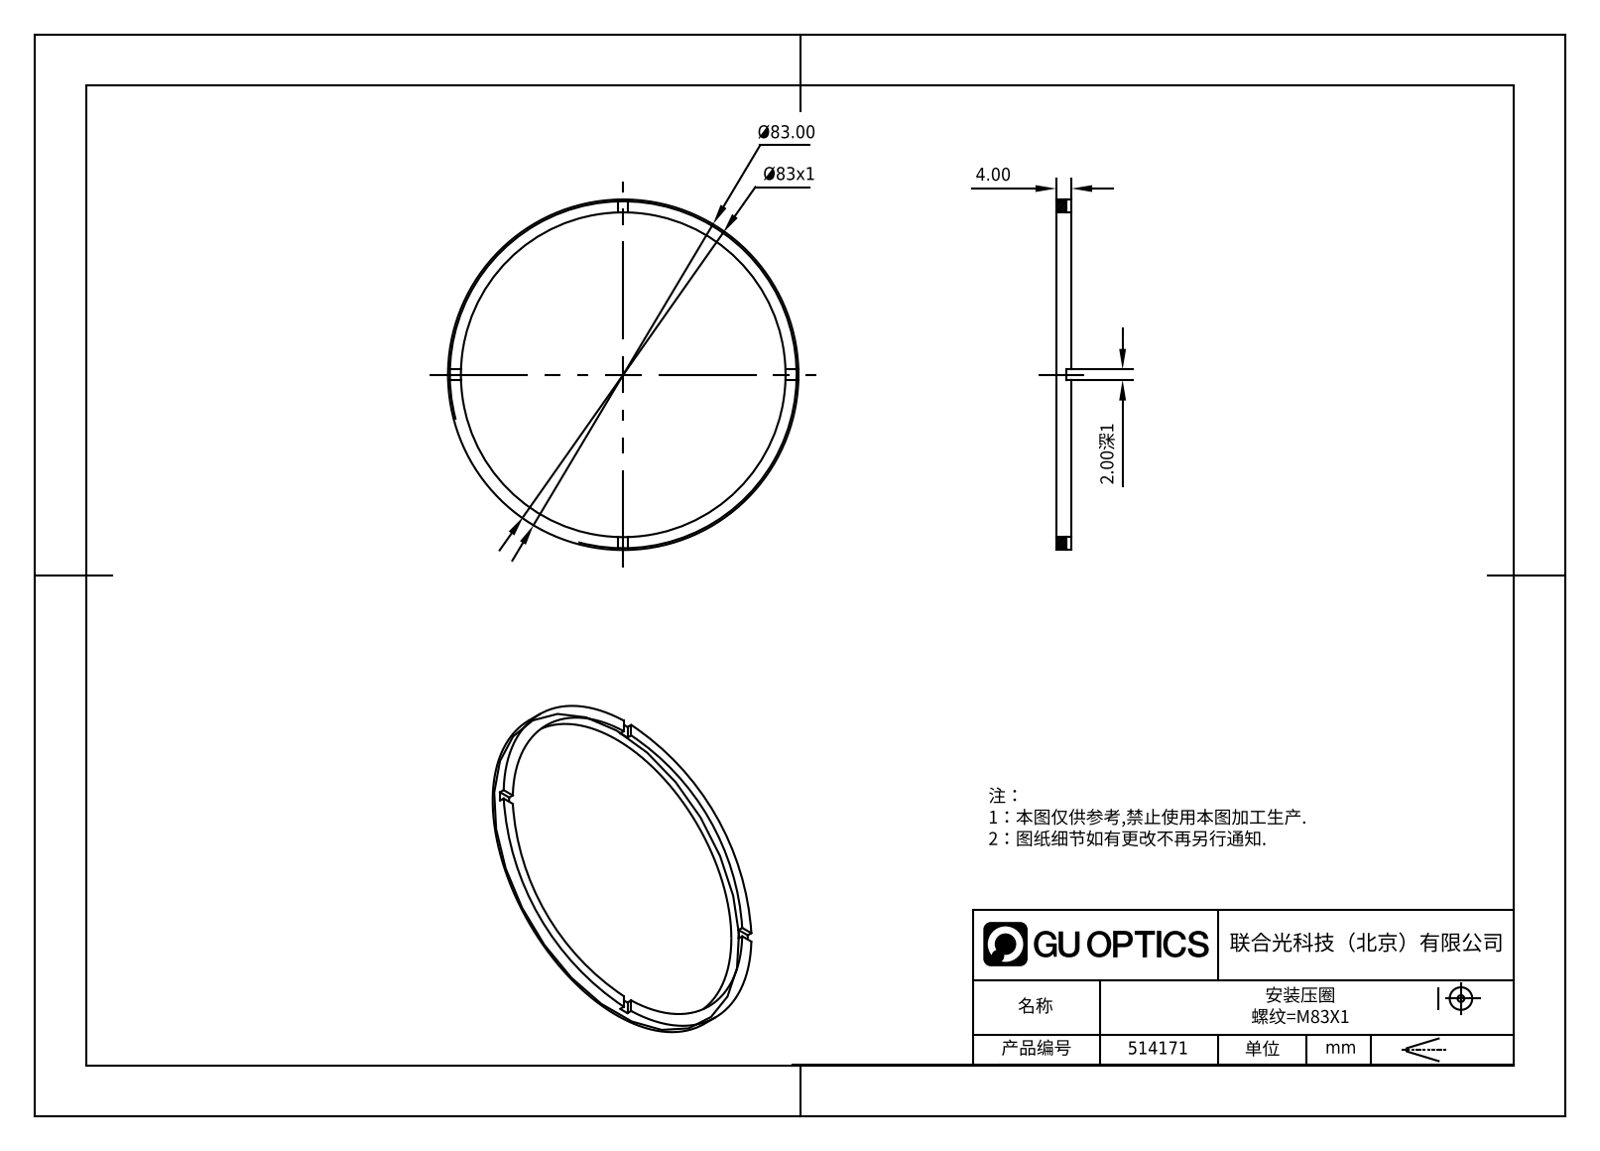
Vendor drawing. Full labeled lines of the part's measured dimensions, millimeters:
Part name (STEP PRODUCT): 514171
STEP written by: SolidWorks 2020 (CONFIG_CONTROL_DESIGN)
Units: millimetres
Bodies: 1 solid, 21 faces (17 planar, 4 cylindrical, 0 other)
Overall size (bounding box): 83 × 83 × 4
Volume: 2 992 mm³ · Surface area: 3 527 mm²
Round holes (diameter × count): ⌀77 ×1
Round bosses / shafts (diameter × count): ⌀83 ×1
Main face-to-face distances: 4, 3, 1, 2
